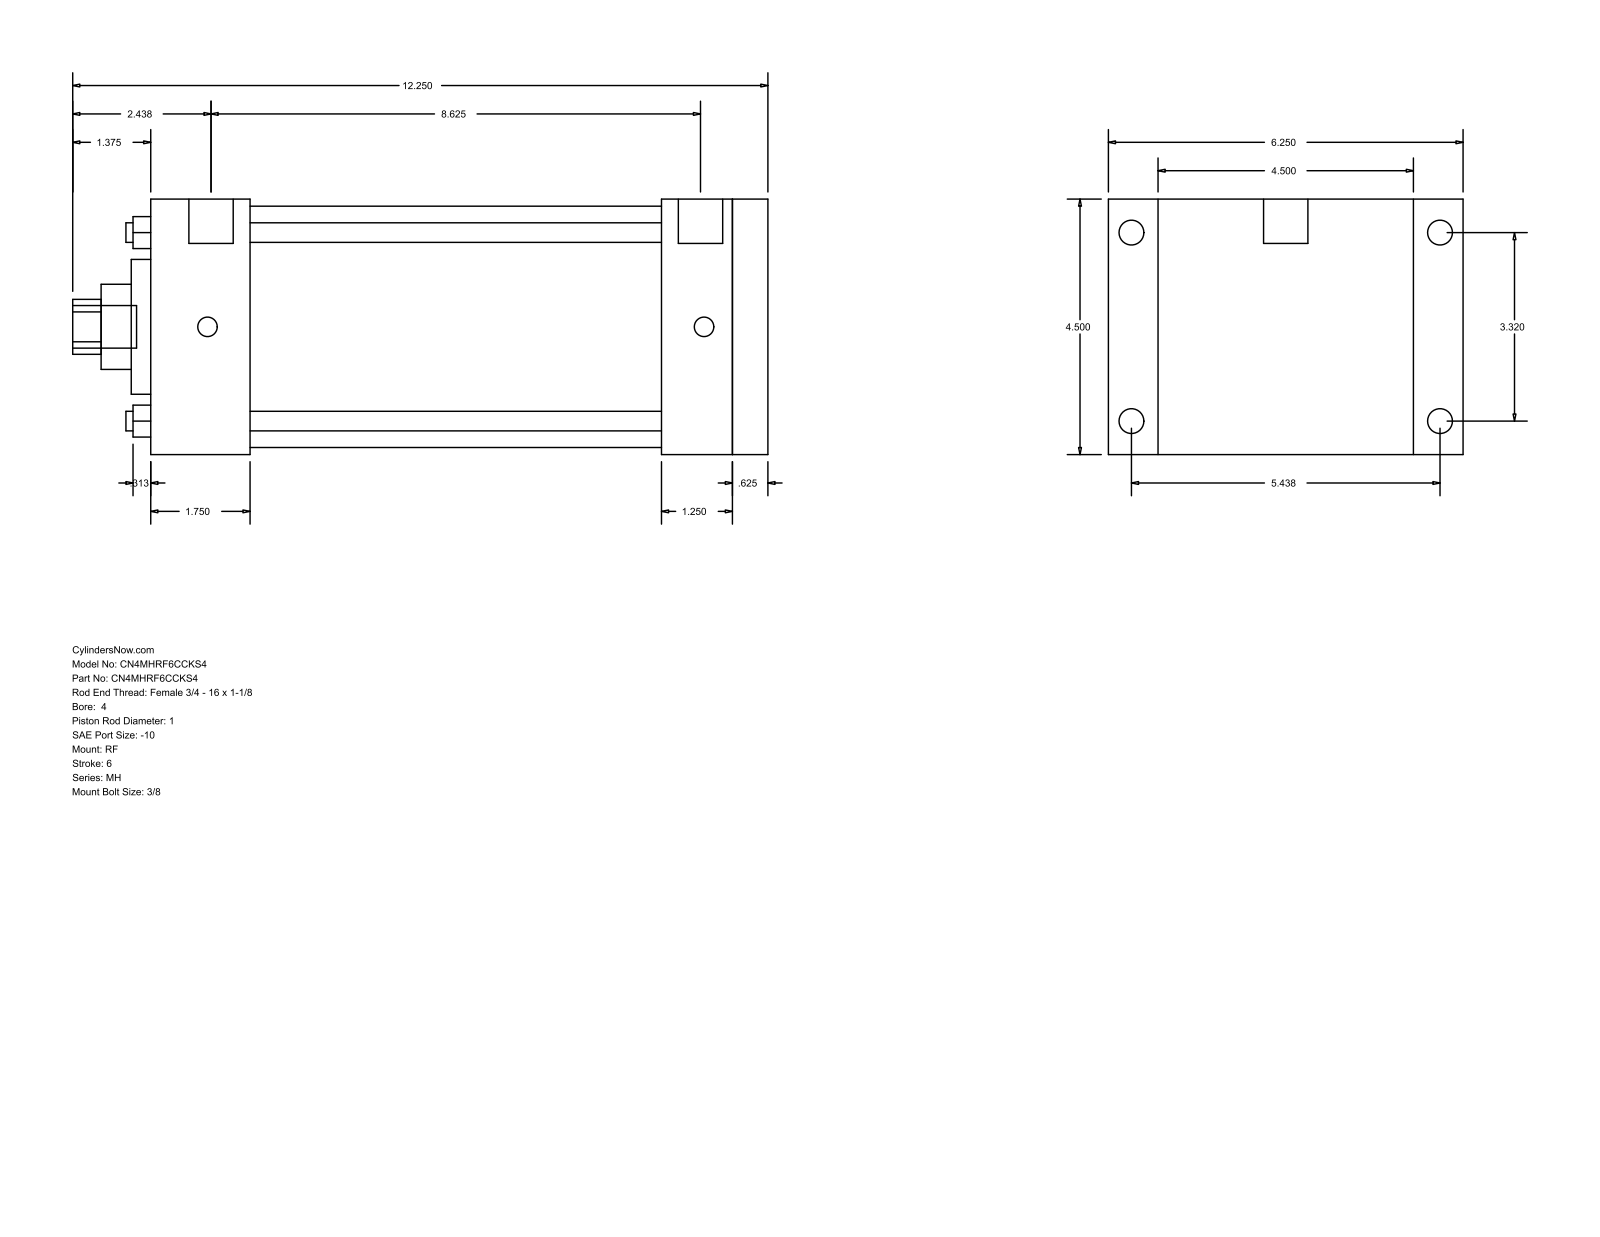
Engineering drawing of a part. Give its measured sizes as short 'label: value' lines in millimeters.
name: MH_RF__0400_1
written by: GSSL Pune (CONFIG_CONTROL_DESIGN)
unit: mm
bodies: 0 solids, 94 faces (65 planar, 29 cylindrical, 0 other)
size: 311.15 × 158.75 × 114.3
holes: 4× ⌀8.76, 1× ⌀25.4, 1× ⌀38.1, 1× ⌀60.33, 1× ⌀107.95
bosses: 4× ⌀11.13, 4× ⌀8.73, 2× ⌀19.84, 1× ⌀19.05
rounds: 1× R12.29
face distances: 114.3, 276.23, 260.35, 15.88, 47.63, 44.46, 215.89, 231.77, 228.6, 184.14
hole spacings: 59.62, 84.32, 119.25
